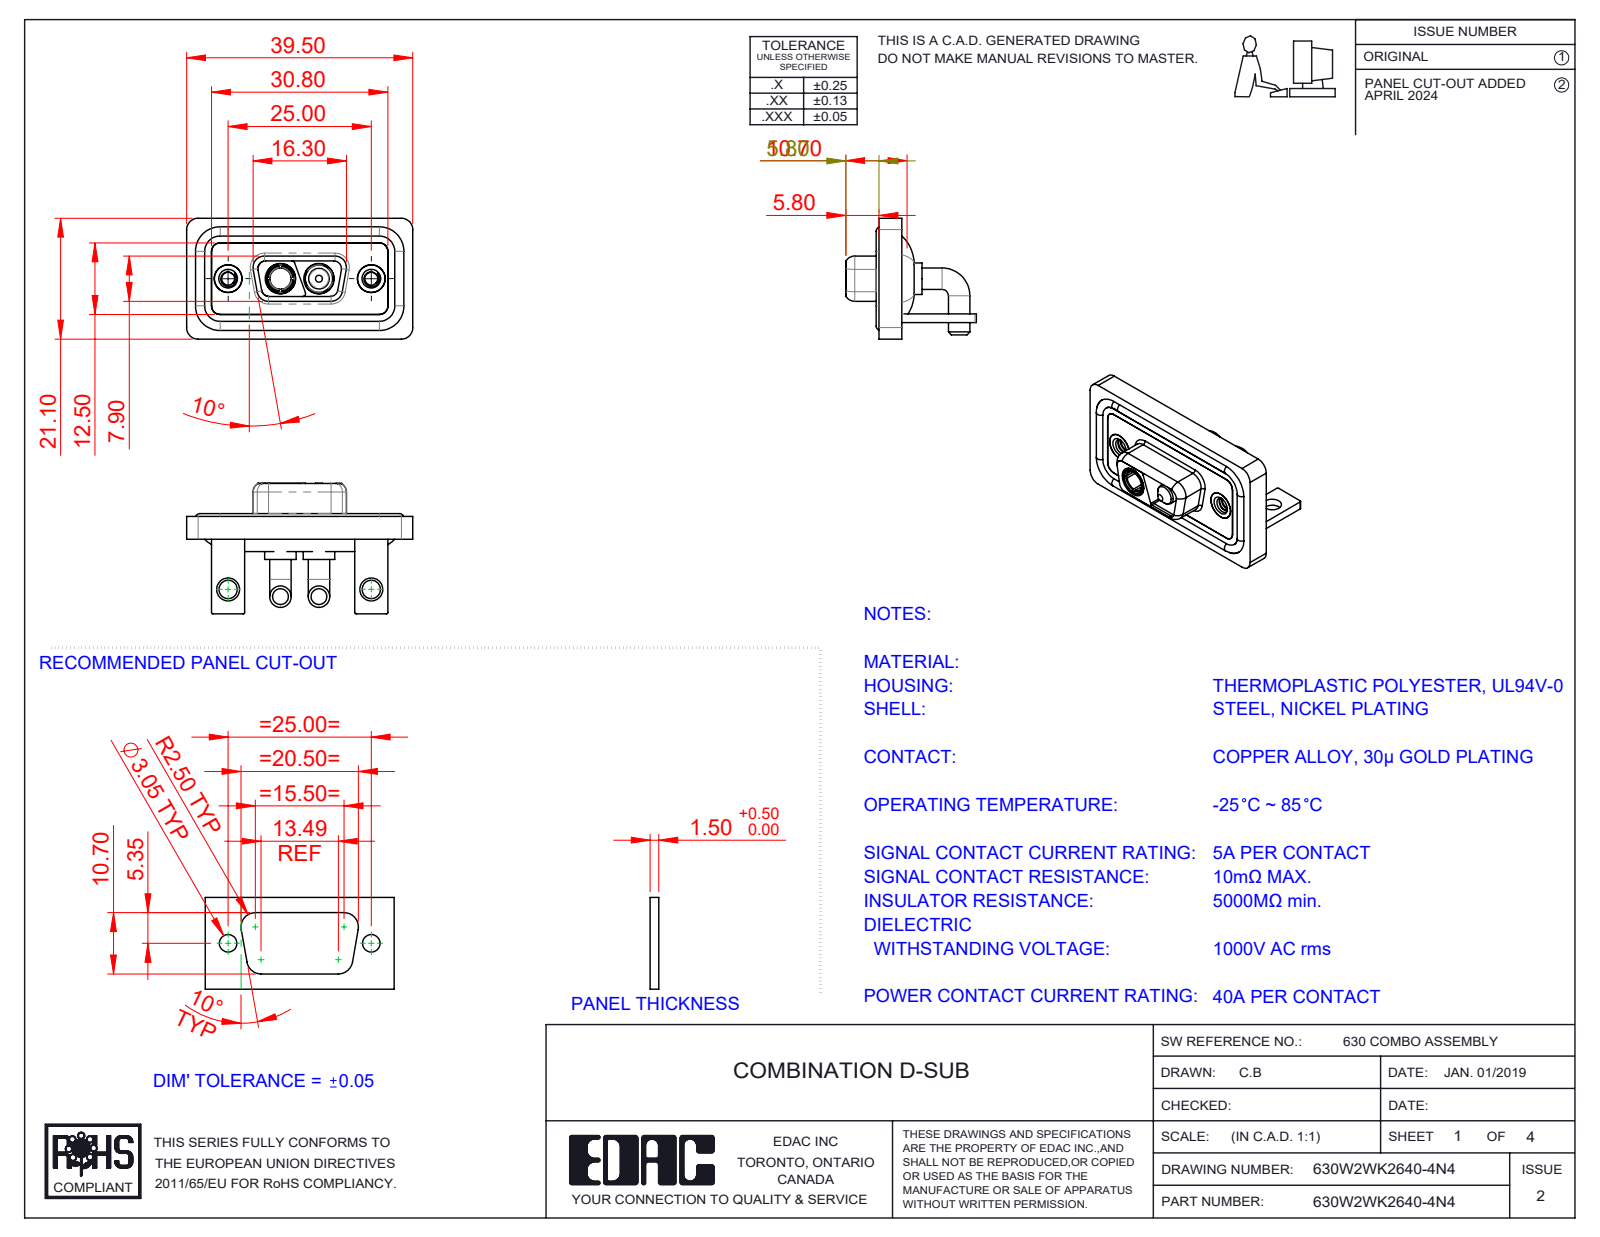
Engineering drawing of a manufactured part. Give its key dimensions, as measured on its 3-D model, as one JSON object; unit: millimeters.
{"part_name": "630Combo Shell Rear_09 Contacts; Power Pin_40A RA; 630Combo Waterproof Housing_09 Contacts; 630Combo Housing_2WK2 (+5 more)", "step_written_by": "SolidWorks 2023 (CONFIG_CONTROL_DESIGN)", "units": "millimeters", "bodies": {"solids": 13, "faces": 556, "planar": 164, "cylindrical": 259, "other": 133}, "overall_size": [39.5, 22.8, 21.1], "volume_mm3": 5219, "surface_area_mm2": 8317, "round_holes": [[4.85, 4], [2.26, 2], [3.2, 2], [4, 2], [4.05, 2], [5, 2], [5.3, 2], [3.7, 1]], "round_bosses_or_shafts": [[3.75, 4], [1.6, 4], [5.5, 2], [5.2, 2], [4.95, 2], [4.8, 2], [4.75, 2], [4.96, 1]], "partial_cylinders_radius": [[2, 19], [1.5, 18], [0.25, 16], [1.35, 8], [1.6, 8], [0.5, 7], [0.6, 4], [0.65, 4]], "face_to_face_distances": [0.4, 2.9, 1.5, 1.1, 3.7, 1.8, 0.8, 2.5, 1.6, 3.1], "hole_center_spacings": [9.14, 15.86, 25, 6.72]}
